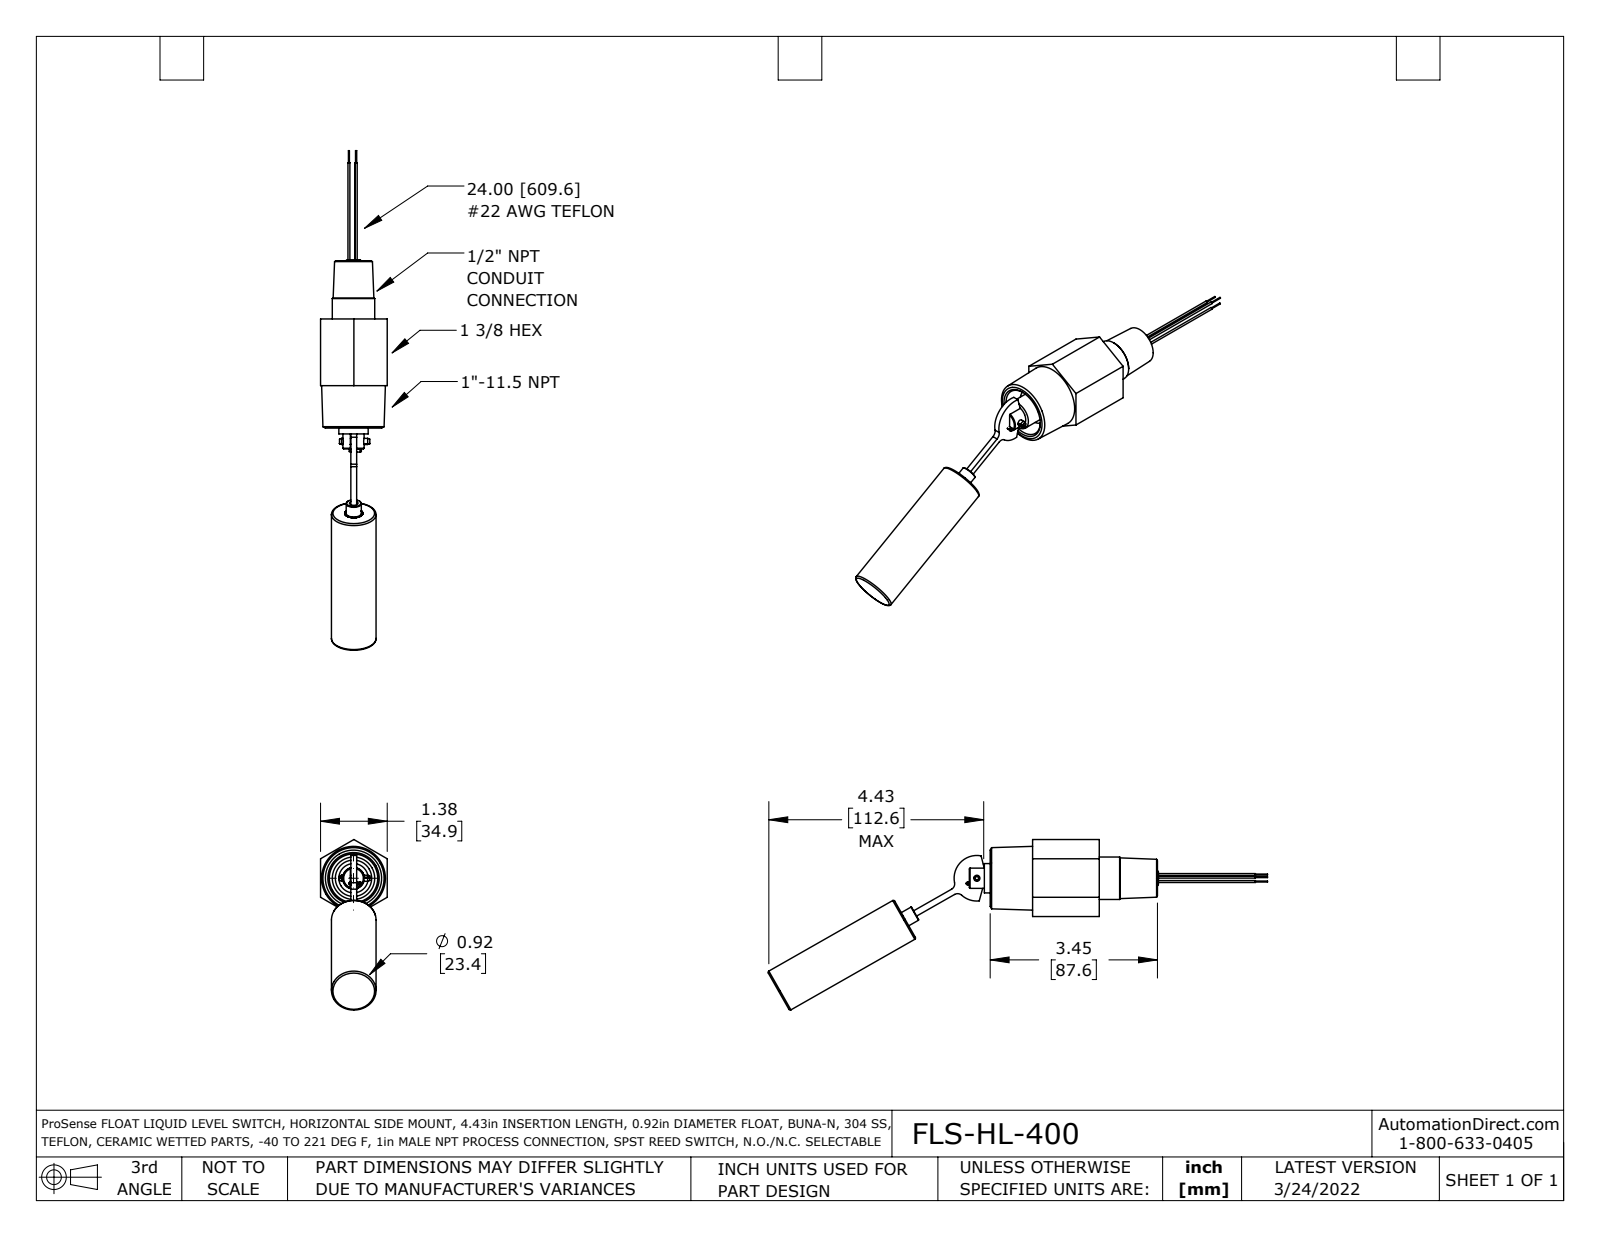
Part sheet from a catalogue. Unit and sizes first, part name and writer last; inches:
Units: inches
Overall size (bounding box): 10.3 × 3.516 × 1.375
Round holes (diameter × count): ⌀0.05 ×3, ⌀0.023 ×1, ⌀0.039 ×1, ⌀0.062 ×1, ⌀0.069 ×1, ⌀0.125 ×1, ⌀0.13 ×1, ⌀0.178 ×1, ⌀0.196 ×1, ⌀0.312 ×1, ⌀0.368 ×1, ⌀0.437 ×1
Round bosses / shafts (diameter × count): ⌀0.04 ×3, ⌀0.02 ×3, ⌀0.92 ×1, ⌀0.875 ×1, ⌀0.75 ×1, ⌀0.605 ×1, ⌀0.312 ×1, ⌀0.25 ×1
Partial cylindrical surfaces — rounded edges, fillets, slot ends (radius × count): R0.125 ×2, R0.188 ×1, R0.47 ×1
Main face-to-face distances: 1.375, 0.25, 0.744, 0.63, 0.12, 0.87, 0.624, 0.75, 3, 1.12
Hole centre spacings: 0.085, 0.094, 0.097, 0.144, 0.159, 0.172, 0.218
Volume: 5.066 in³ · Surface area: 55.46 in²
Bodies: 15 solids, 387 faces (184 planar, 146 cylindrical, 57 other)
Part name (STEP PRODUCT): ADM4190-BU nc coord fxt
STEP written by: SolidWorks 2021 (AUTOMOTIVE_DESIGN)
